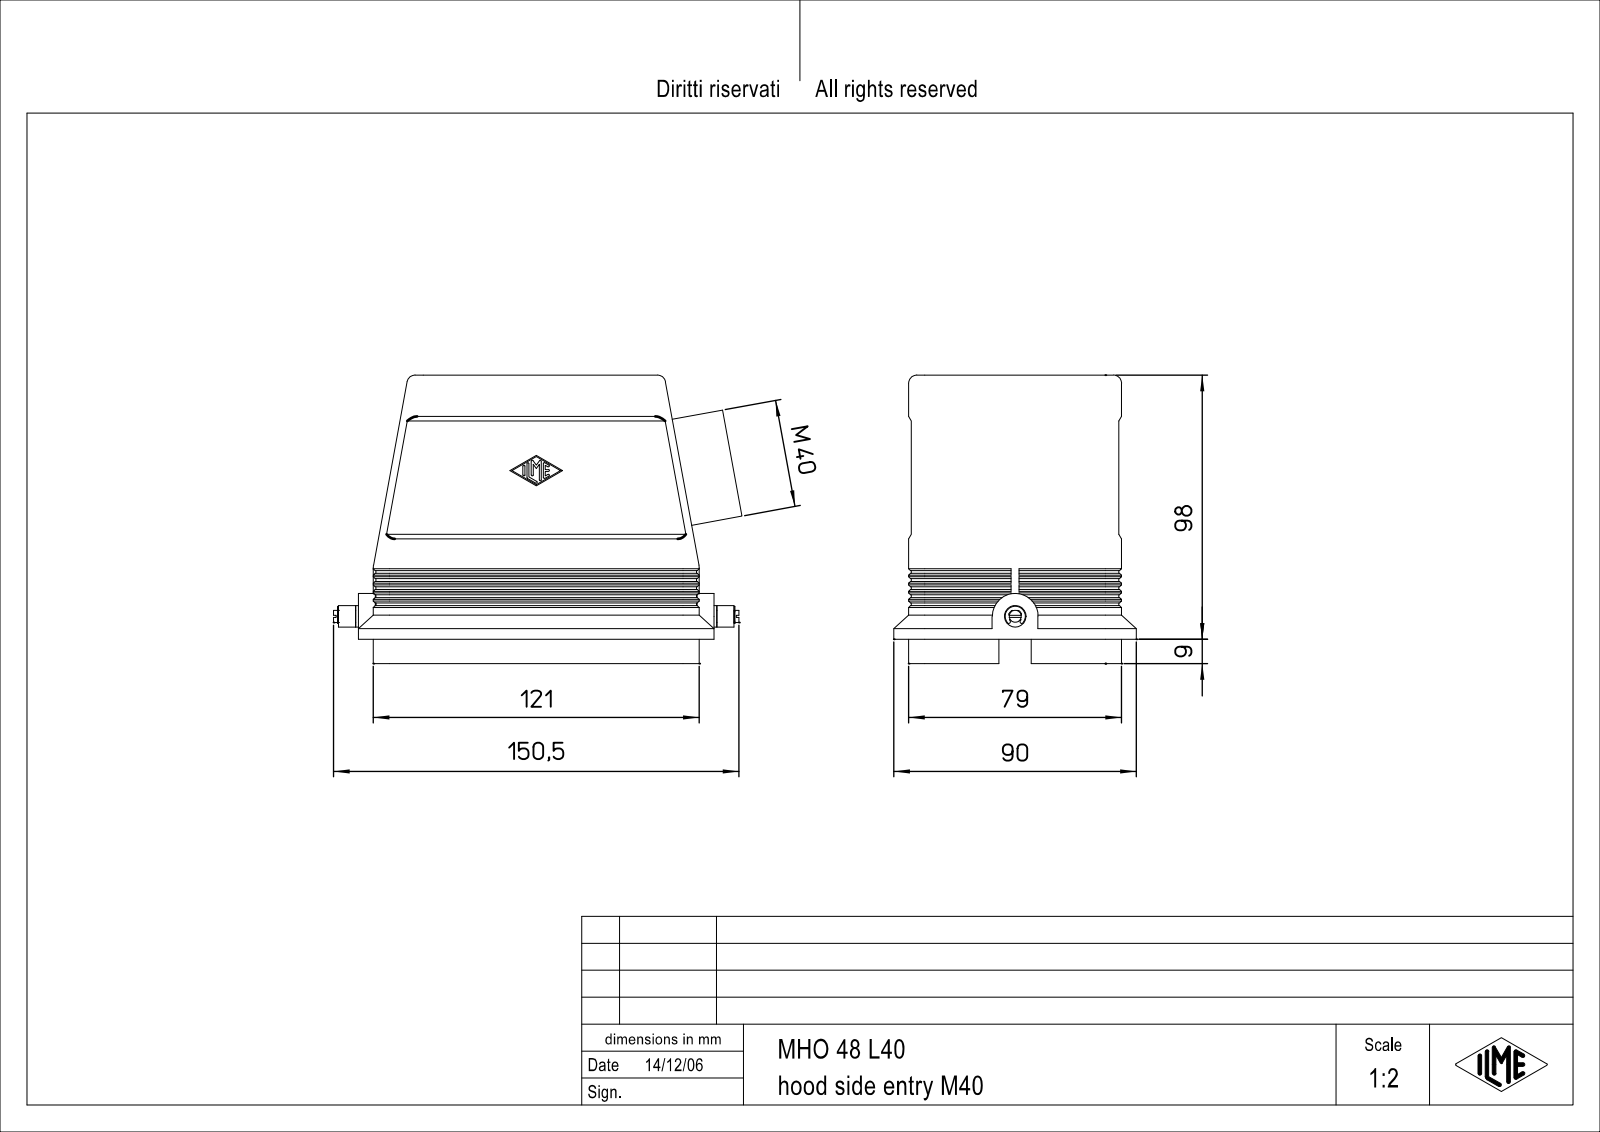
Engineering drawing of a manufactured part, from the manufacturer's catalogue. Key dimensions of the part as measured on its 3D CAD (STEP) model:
Part name (STEP PRODUCT): CH_MH Tüllengehäuse Verschluss für 1 Bügel 104_62 Teil 1
STEP written by: Autodesk Inventor 7 (AUTOMOTIVE_DESIGN)
Units: millimetres
Bodies: 1 solid, 684 faces (242 planar, 187 cylindrical, 255 other)
Overall size (bounding box): 150.5 × 107 × 90
Volume: 249 216 mm³ · Surface area: 101 521 mm²
Round holes (diameter × count): ⌀2.46 ×4, ⌀3.5 ×4, ⌀6 ×1, ⌀38 ×1, ⌀40 ×1, ⌀57 ×1
Round bosses / shafts (diameter × count): ⌀55 ×1, ⌀49 ×1, ⌀8 ×1, ⌀4.5 ×1, ⌀3.5 ×1
Partial cylindrical surfaces — rounded edges, fillets, slot ends (radius × count): R0.38 ×14, R2 ×12, R6 ×10, R0.5 ×4, R3 ×4, R11.5 ×4, R0.95 ×3, R0.6 ×2
Main face-to-face distances: 72, 3.5, 75.5, 13, 2.5, 74.5, 1, 78, 79, 8.5
Hole centre spacings: 27, 104, 107.45
